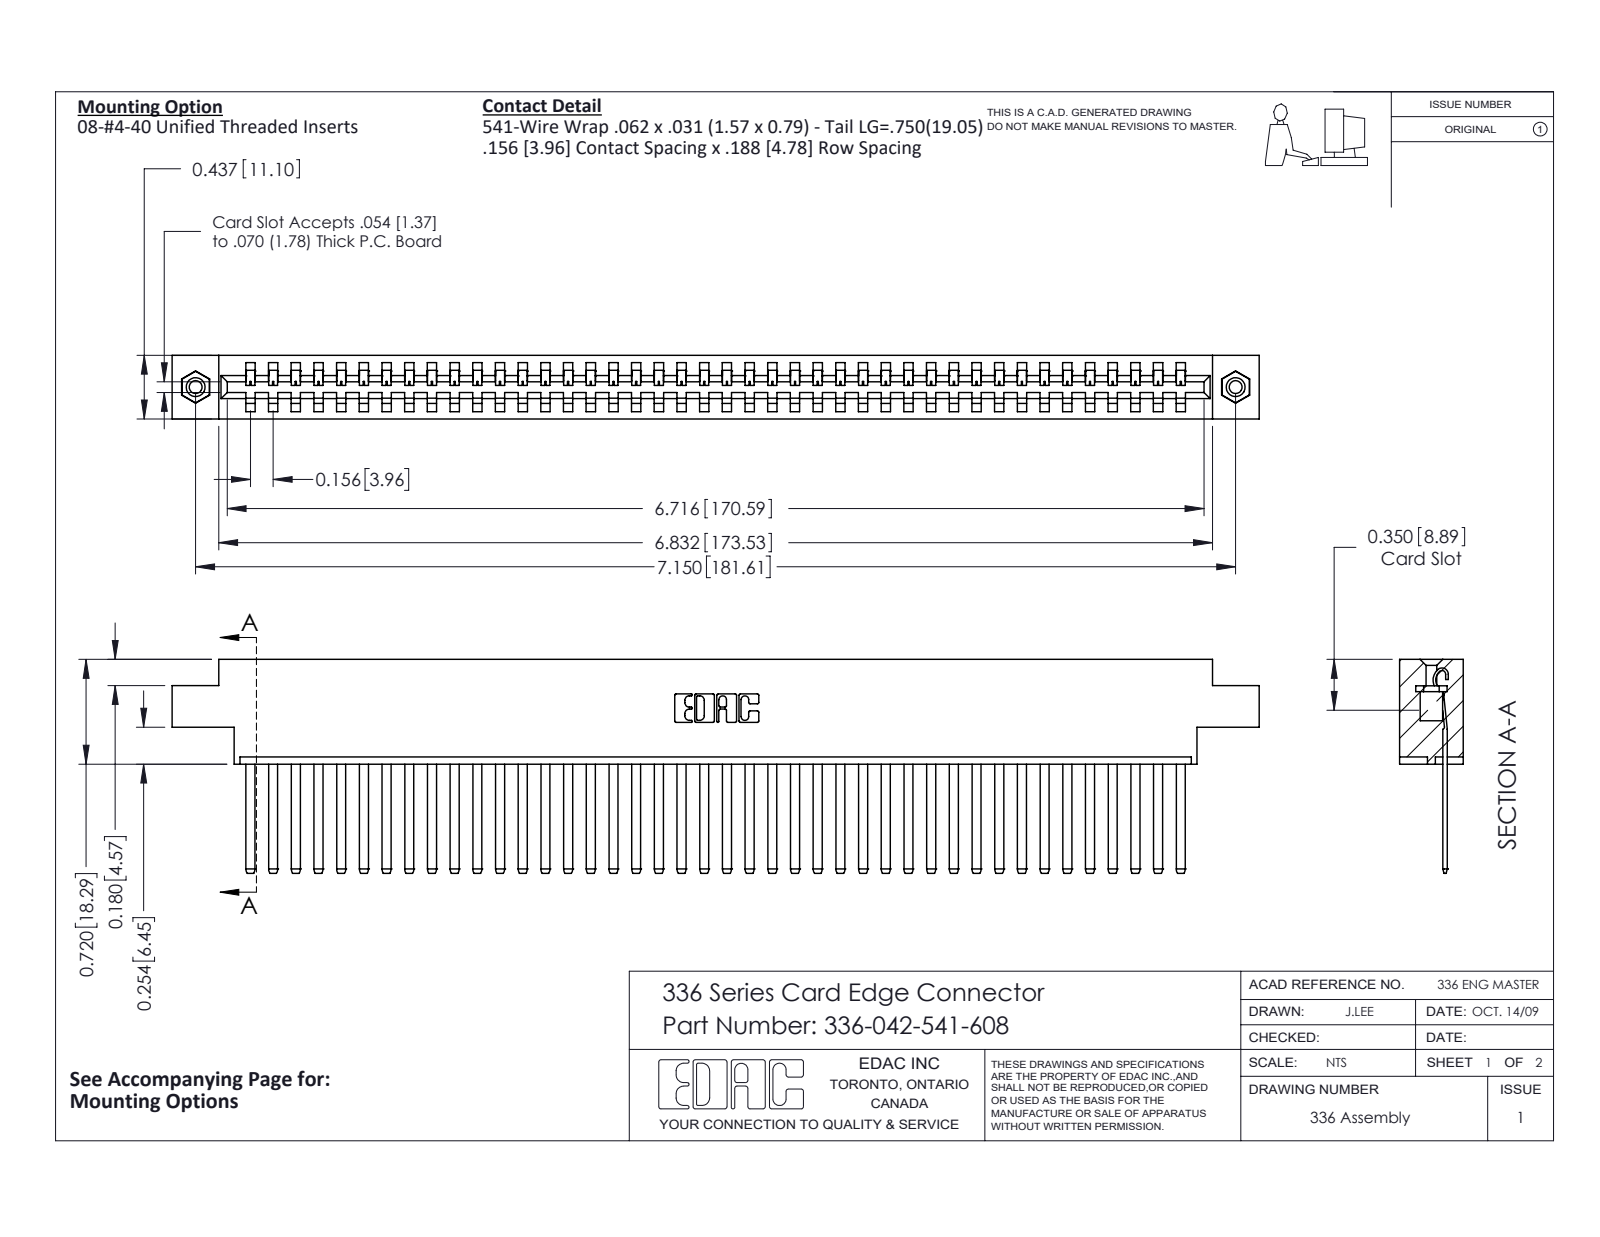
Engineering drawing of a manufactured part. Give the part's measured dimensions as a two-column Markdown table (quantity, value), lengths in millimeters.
| quantity | value |
| --- | --- |
| part name | 345-250-001_345-250-003-102; 336 Part_Offset - .156 Dia - TI; 336-290-001_336-290-541; 336-042-541-608 |
| STEP written by | SolidWorks 2020 (CONFIG_CONTROL_DESIGN) |
| units | millimeters |
| bodies | 45 solids, 2278 faces (1534 planar, 728 cylindrical, 16 other) |
| overall size | 189.8 × 37.3 × 11.1 |
| volume | 27 640 mm³ |
| surface area | 30 210 mm² |
| round holes (diameter × count) | 2.3 × 2, 3.2 × 2, 4 × 2 |
| round bosses / shafts (diameter × count) | 3.9 × 2 |
| partial cylindrical surfaces (radius × count) | 0.1 × 84, 1.4 × 84, 0.3 × 22, 0.2 × 6, 0.8 × 6, 0.7 × 3, 0.6 × 2, 1 × 2 |
| main face-to-face distances | 11.1, 4.6, 8.3, 3.6, 7.5, 2.8, 0.8, 6.5, 1.3, 3.3 |
| hole center spacings | 181.6 |
